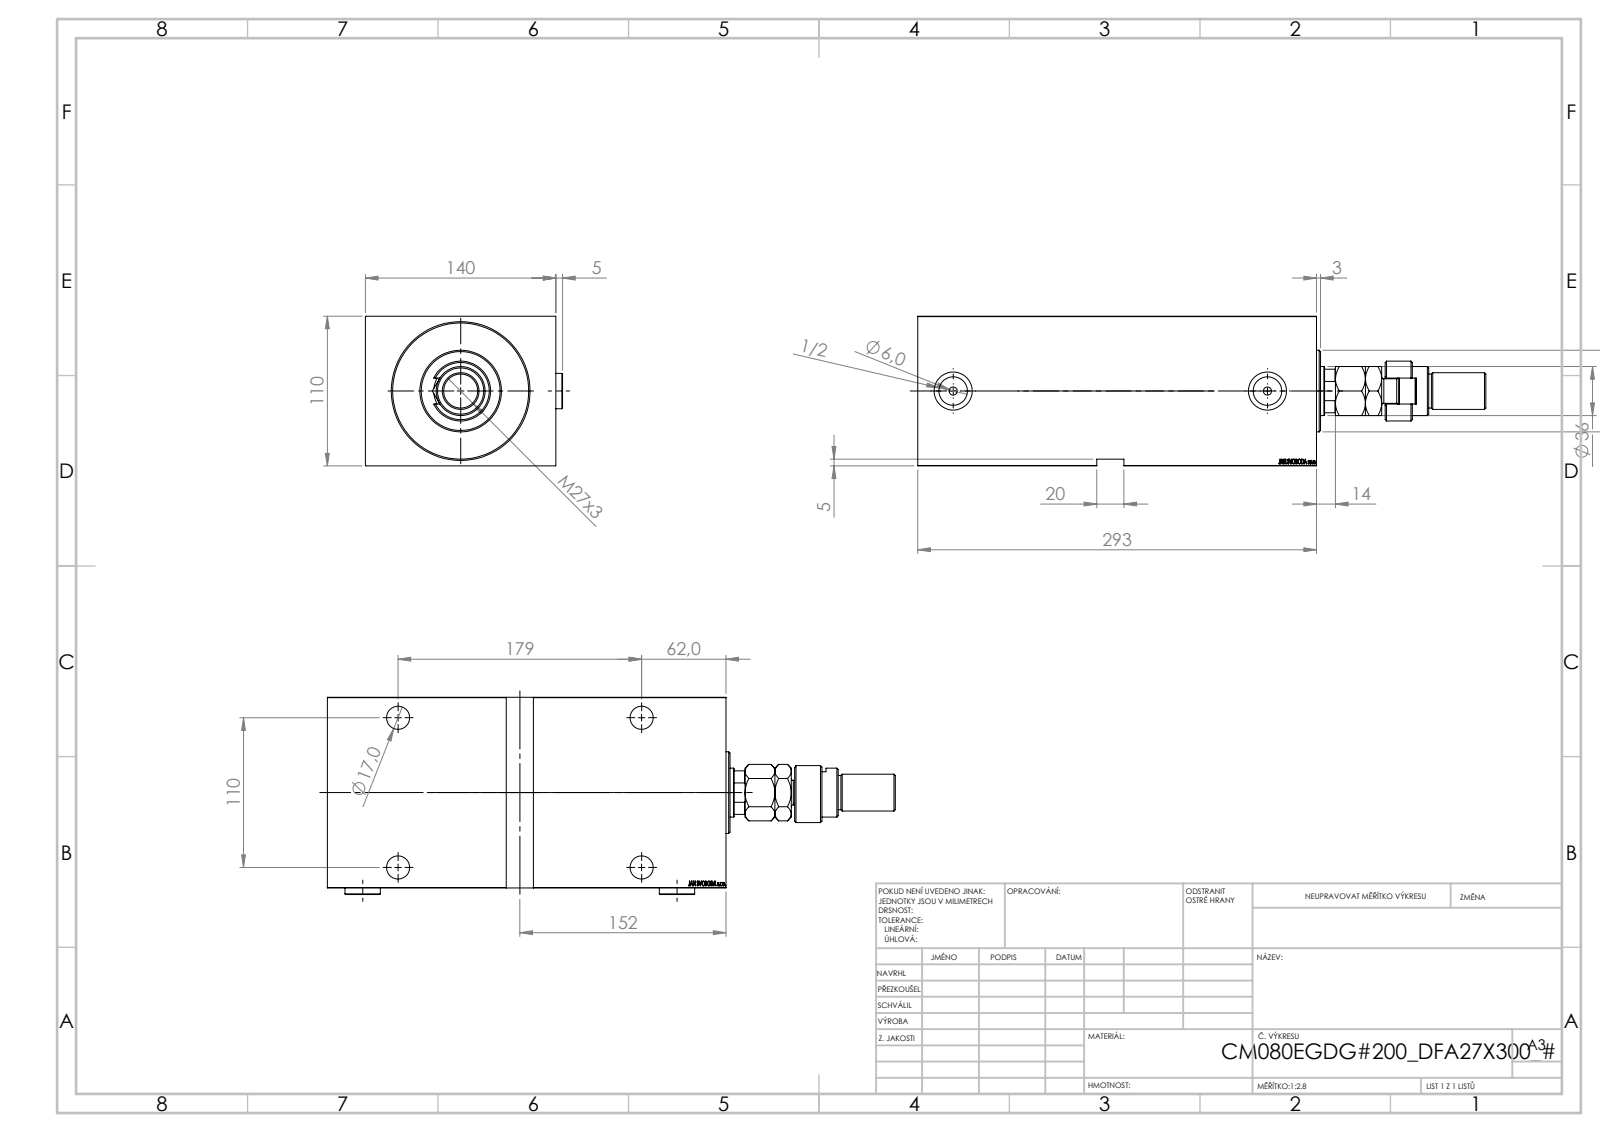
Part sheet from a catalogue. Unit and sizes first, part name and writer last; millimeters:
Units: millimetres
Overall size (bounding box): 417.5 × 144.9 × 110
Round holes (diameter × count): ⌀17 ×4, ⌀25 ×4, ⌀6 ×2, ⌀20.96 ×2, ⌀28 ×2, ⌀25.5 ×1, ⌀39.5 ×1, ⌀80 ×1, ⌀100 ×1
Round bosses / shafts (diameter × count): ⌀26 ×2, ⌀82 ×1, ⌀60 ×1, ⌀44 ×1, ⌀36 ×1, ⌀28 ×1, ⌀27 ×1, ⌀25 ×1
Partial cylindrical surfaces — rounded edges, fillets, slot ends (radius × count): R9.5 ×1, R15 ×1, R17.5 ×1
Main face-to-face distances: 110, 140, 293, 21, 272, 5, 288, 267, 79, 276.4
Hole centre spacings: 110, 179, 210.1, 231
Volume: 3 667 000 mm³ · Surface area: 373 581 mm²
Bodies: 7 solids, 997 faces (474 planar, 81 cylindrical, 442 other)
Part name (STEP PRODUCT): FEMALE_PART_FOR_DFA; V450CM_E_VCP; V450CM_VC_B; MFA (+2 more)
STEP written by: SolidWorks 2019 (CONFIG_CONTROL_DESIGN)
